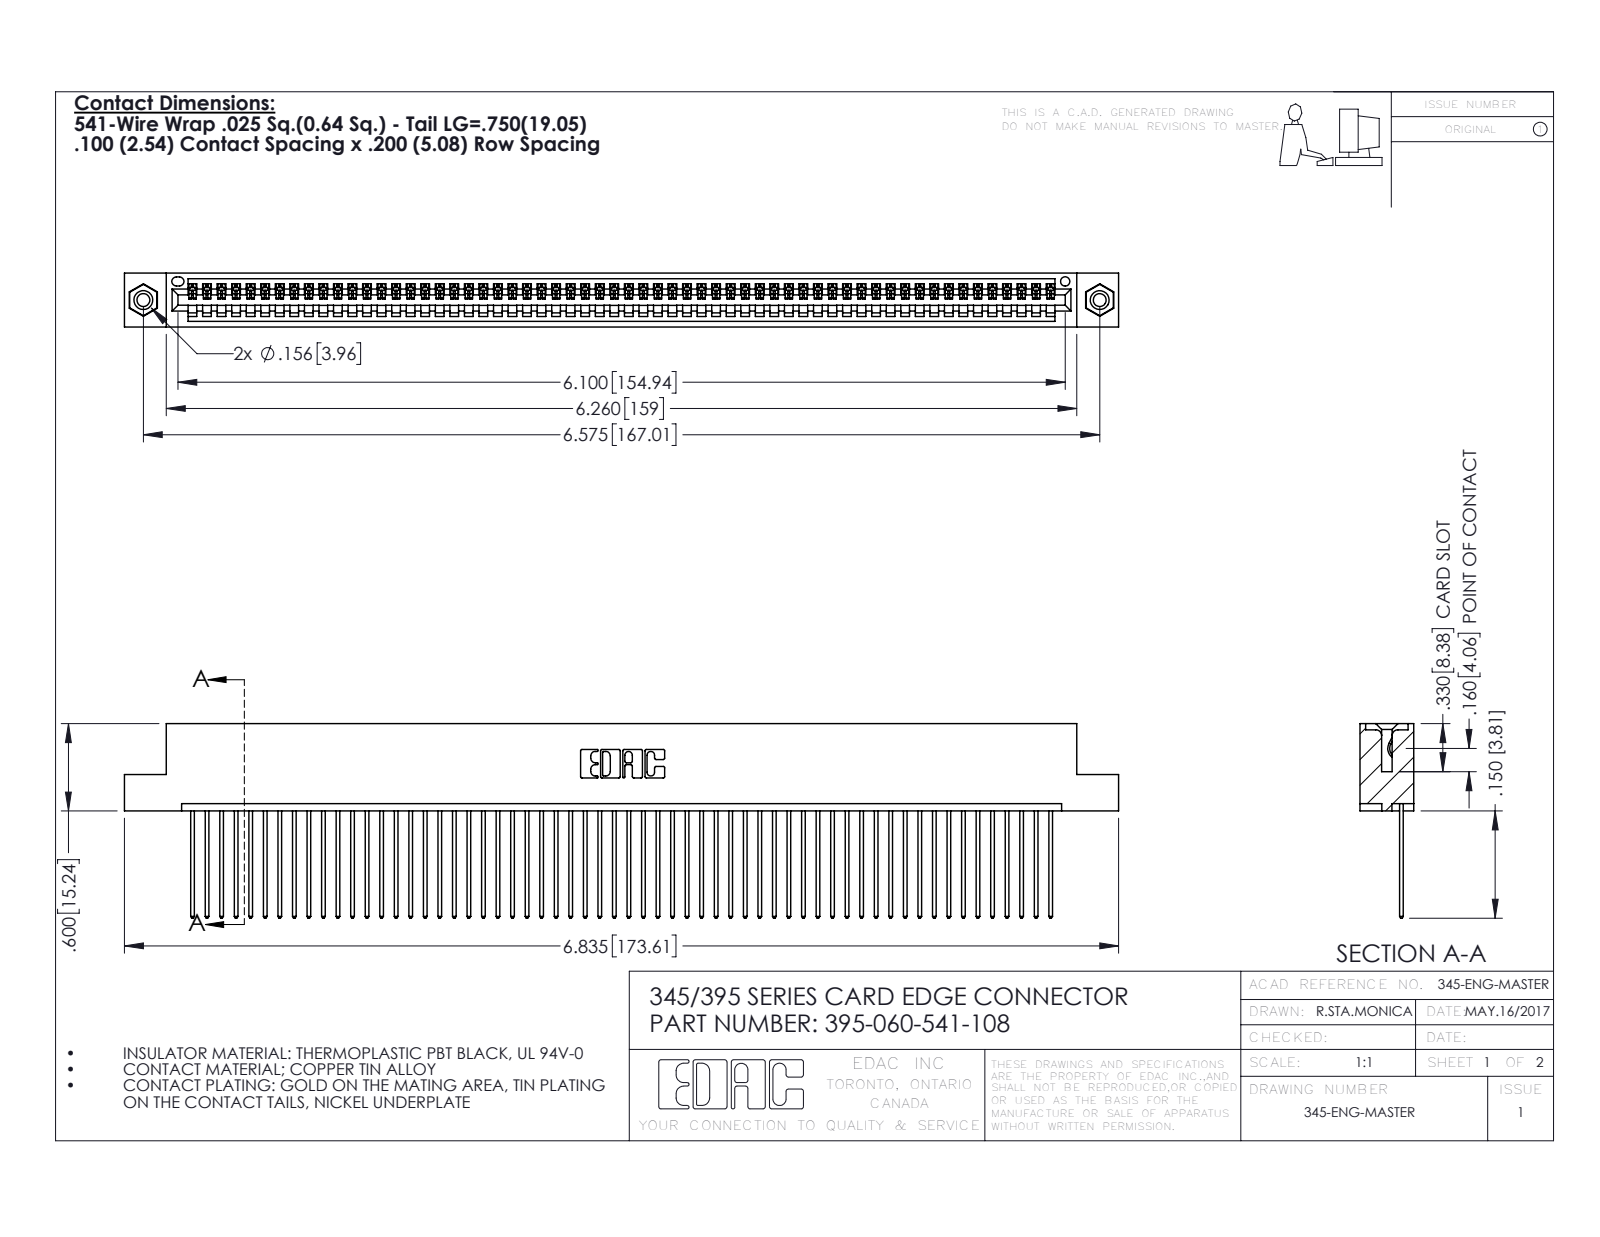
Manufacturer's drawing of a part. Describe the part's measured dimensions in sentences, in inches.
The part is named "345-250-001_345-250-003-102; 345-292-001_345-293-141; 345 Part_Flush Mounting Lugs - 0.156 Dia-TI; 395-060-541-108". Its 3-D file was written by "SolidWorks 2016 (CONFIG_CONTROL_DESIGN)". It is 63 solids with 3666 faces: 2512 planar, 1138 cylindrical and 16 other. Overall it measures 6.835 by 1.337 by 0.37 inches. Its volume is 1.027 cubic inches and its surface area 36.88 square inches. Round holes: 2 of diameter 0.089, 2 of diameter 0.125, 2 of diameter 0.156, 1 of diameter 0.064. Round bosses or shafts: 2 of diameter 0.155. Partial cylindrical surfaces (rounded edges, fillets, slot ends): 120 of radius 0.006, 120 of radius 0.01, 22 of radius 0.01, 6 of radius 0.007, 6 of radius 0.031, 3 of radius 0.026, 2 of radius 0.031, 2 of radius 0.04. The main face-to-face distances are 0.072, 0.298, 0.098, 0.272, 0.025, 0.37, 0.2, 0.225, 0.149, 0.072. The hole center spacings are 0.27, 6.339, 6.575.
